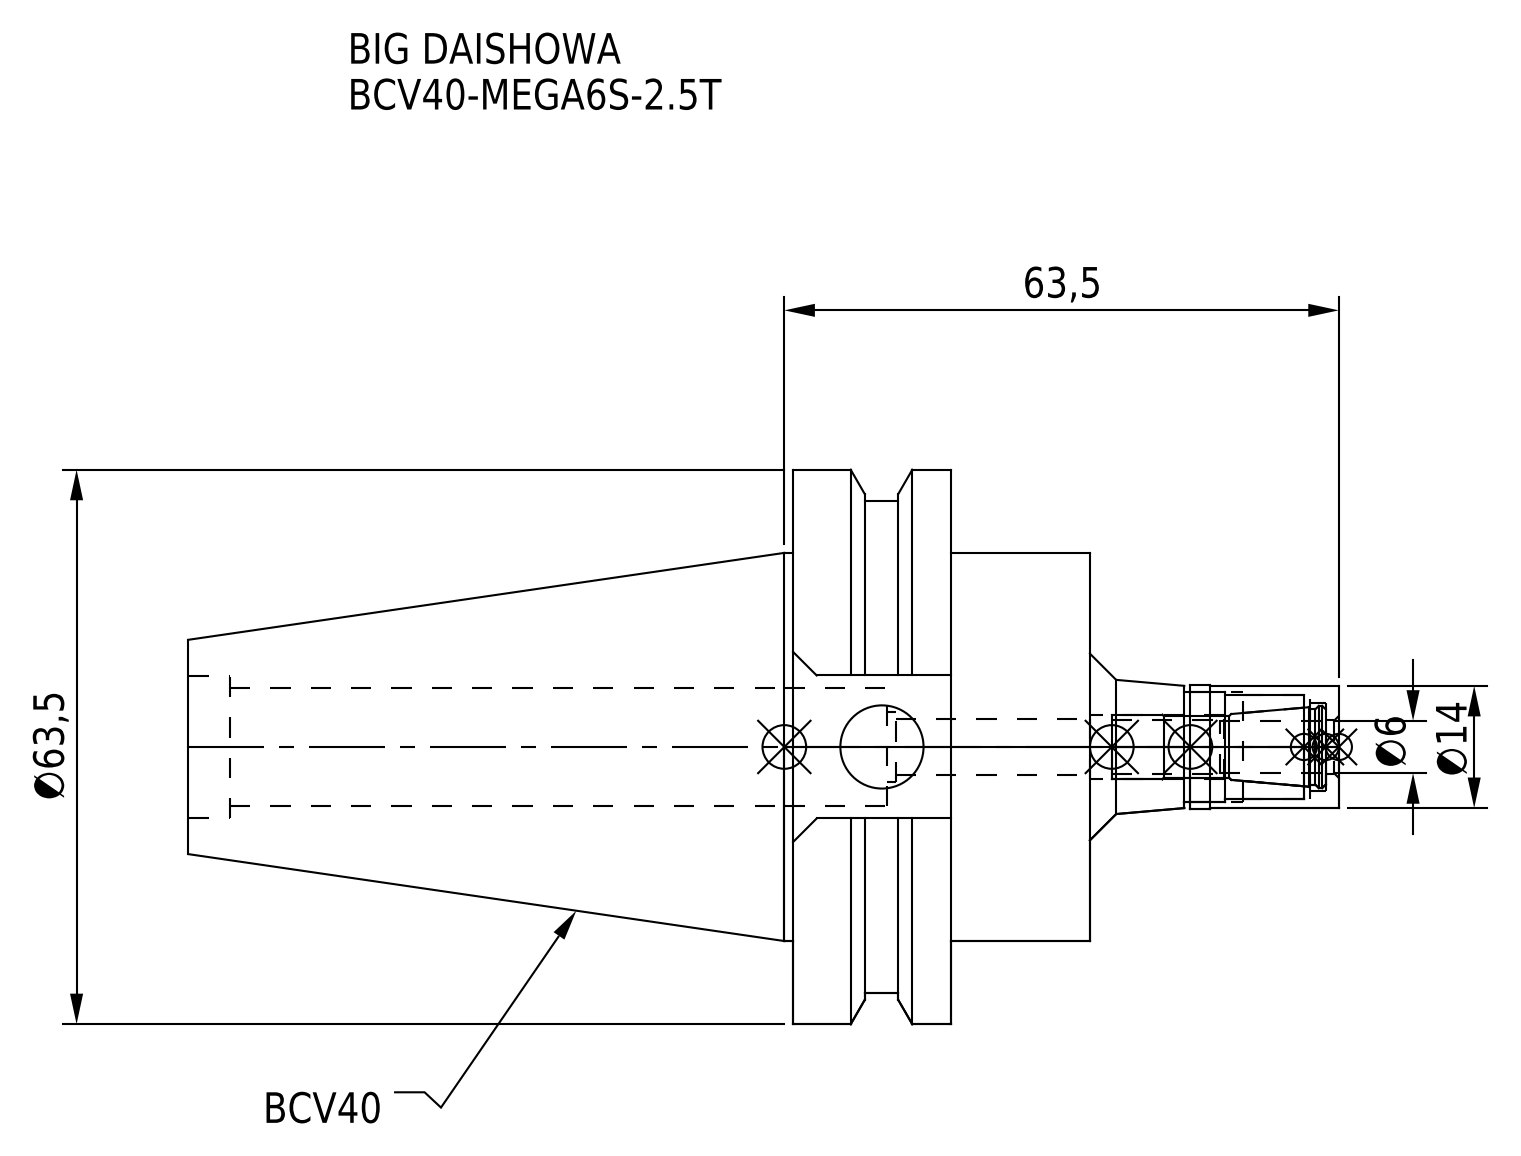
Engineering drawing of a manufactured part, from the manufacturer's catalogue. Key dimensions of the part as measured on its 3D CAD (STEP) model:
Part name (STEP PRODUCT): BCV40-MEGA6S-2_5T-060.stp; BCV40-MEGA6S-2_5T_1.stp; BCV40MS06025T-060_ASM.stp; BCV40-MEGA6S-2_5T-060-FreeParts (+3 more)
STEP written by: SolidWorks 2019 (CONFIG_CONTROL_DESIGN)
Units: millimetres
Bodies: 2 solids, 86 faces (32 planar, 40 cylindrical, 14 other)
Overall size (bounding box): 131.75 × 63.5 × 61.35
Volume: 132 271 mm³ · Surface area: 26 186 mm²
Round holes (diameter × count): ⌀6.1 ×1, ⌀6.4 ×1, ⌀7.4 ×1, ⌀8 ×1, ⌀9.53 ×1, ⌀10 ×1, ⌀12 ×1, ⌀12.5 ×1, ⌀13.6 ×1, ⌀16.32 ×1
Round bosses / shafts (diameter × count): ⌀63.5 ×1, ⌀56.36 ×1, ⌀44.45 ×1, ⌀14.3 ×1, ⌀14 ×1
Main face-to-face distances: 18.05, 15.95, 34, 103.25, 87.3, 69.25, 47.55, 16.38, 6, 25.79
